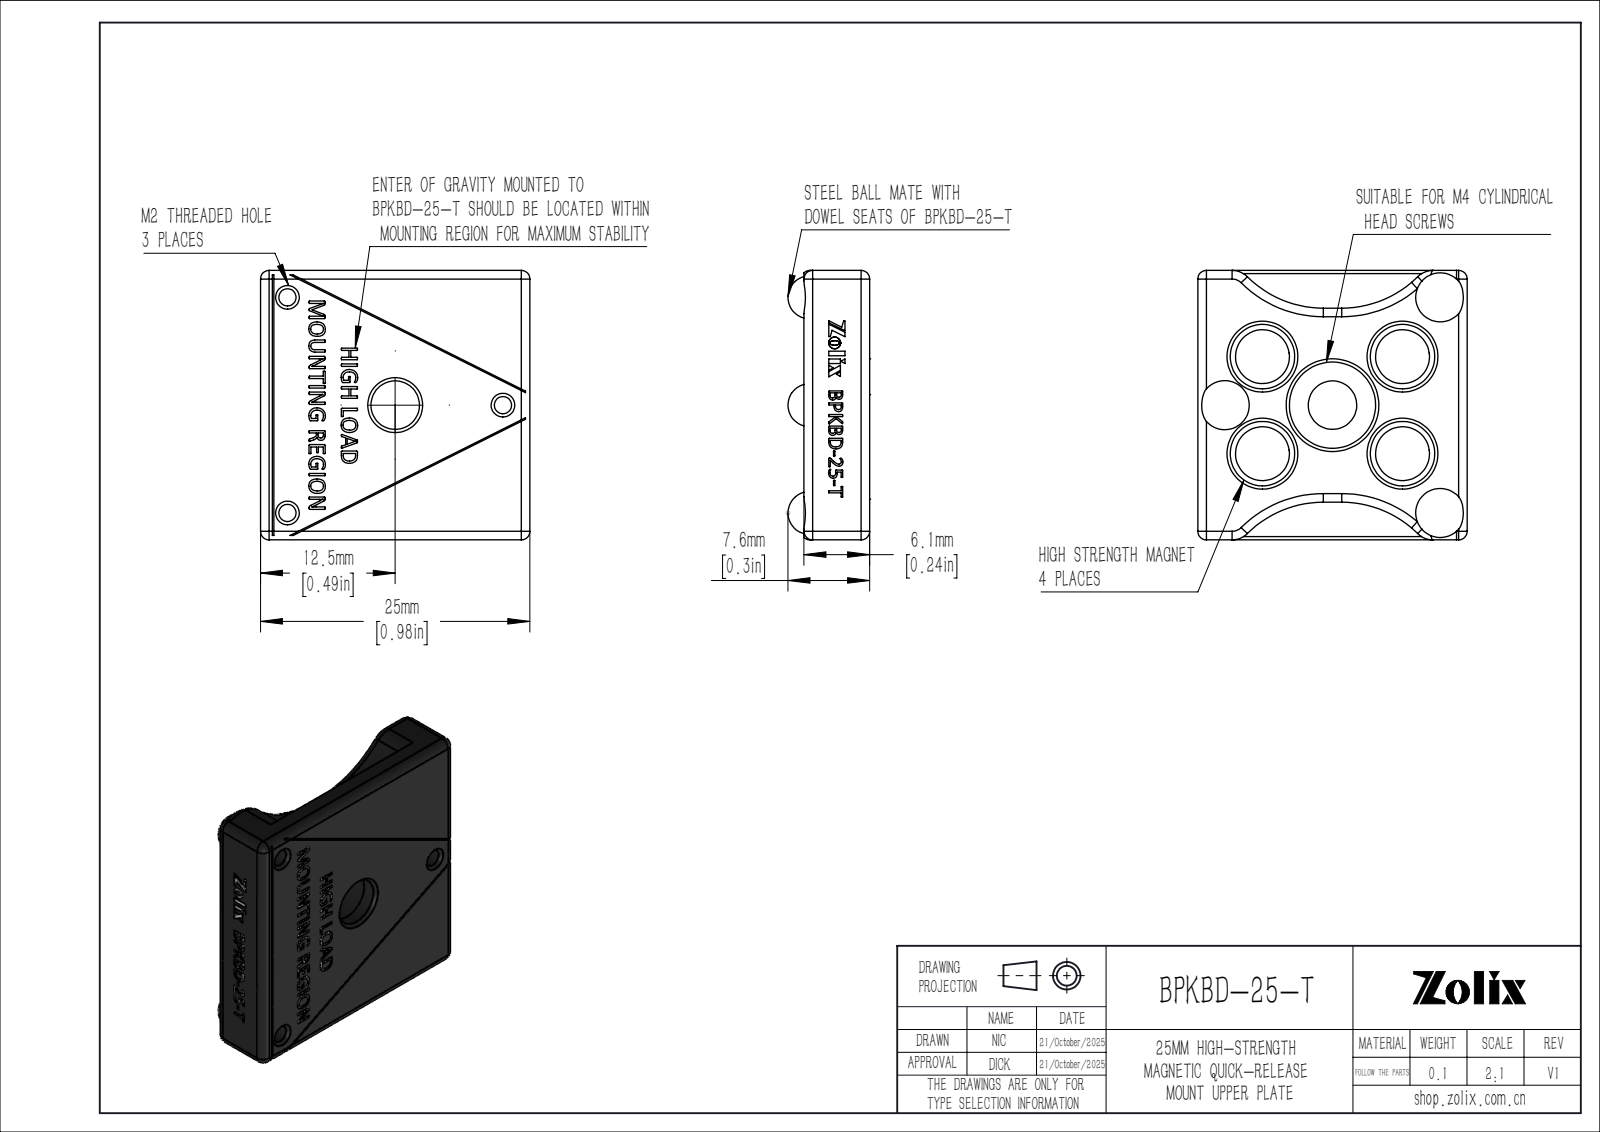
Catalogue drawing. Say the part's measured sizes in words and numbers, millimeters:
The part is named "BPKBD-25-T; 3.98ёЦЗт; 6×3圆柱磁铁; 顶板". Its 3-D file was written by "SolidWorks 2020 (CONFIG_CONTROL_DESIGN)". It is 8 solids with 833 faces: 437 planar, 56 cylindrical and 340 other. Overall it measures 25 by 25 by 7.58 millimeters. Its volume is 3 179 cubic millimeters and its surface area 2 805 square millimeters. Round holes: 4 of diameter 5.98, 3 of diameter 1.6, 3 of diameter 3.95, 1 of diameter 4.5, 1 of diameter 8. Round bosses or shafts: 4 of diameter 6. Partial cylindrical surfaces (rounded edges, fillets, slot ends): 14 of radius 0.8, 4 of radius 2, 4 of radius 10. The main face-to-face distances are 6.1, 3, 3.1, 25, 2.5, 3.6, 0.6, 1.1, 0.5, 2.1. The hole center spacings are 7.91, 5.7, 6.52, 9, 13, 14.14, 14.92, 15.81.
